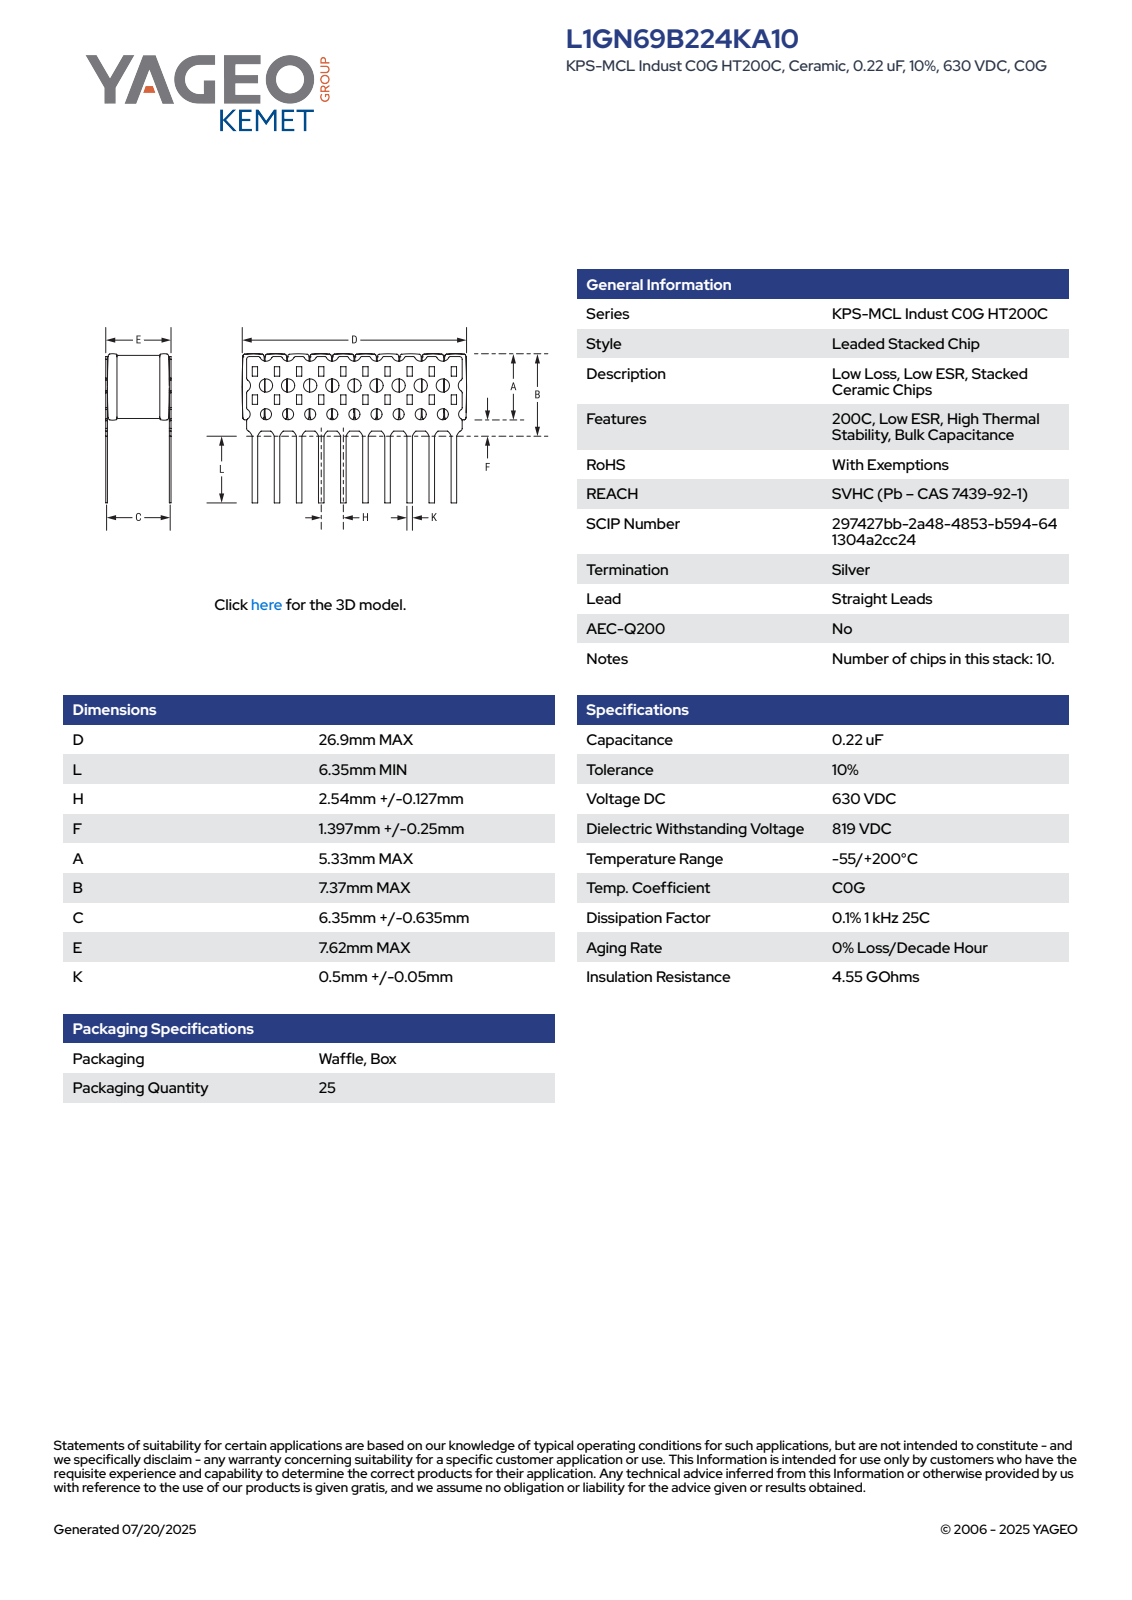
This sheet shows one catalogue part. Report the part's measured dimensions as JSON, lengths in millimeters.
{"part_name": "CCSS_KLSS10_D26.9L6.35H2.667F1.647A5.33B7.37C6.985E7.62K0.55", "step_written_by": "SolidWorks 2014 (AUTOMOTIVE_DESIGN)", "units": "millimeters", "bodies": {"solids": 7, "faces": 298, "planar": 298, "cylindrical": 0, "other": 0}, "overall_size": [26.92, 13.02, 6.99], "volume_mm3": 1017, "surface_area_mm2": 1484, "face_to_face_distances": [2.69, 8.08, 10.77, 13.46, 6.99, 2.49, 5.38, 5.39, 7.88, 10.57]}
